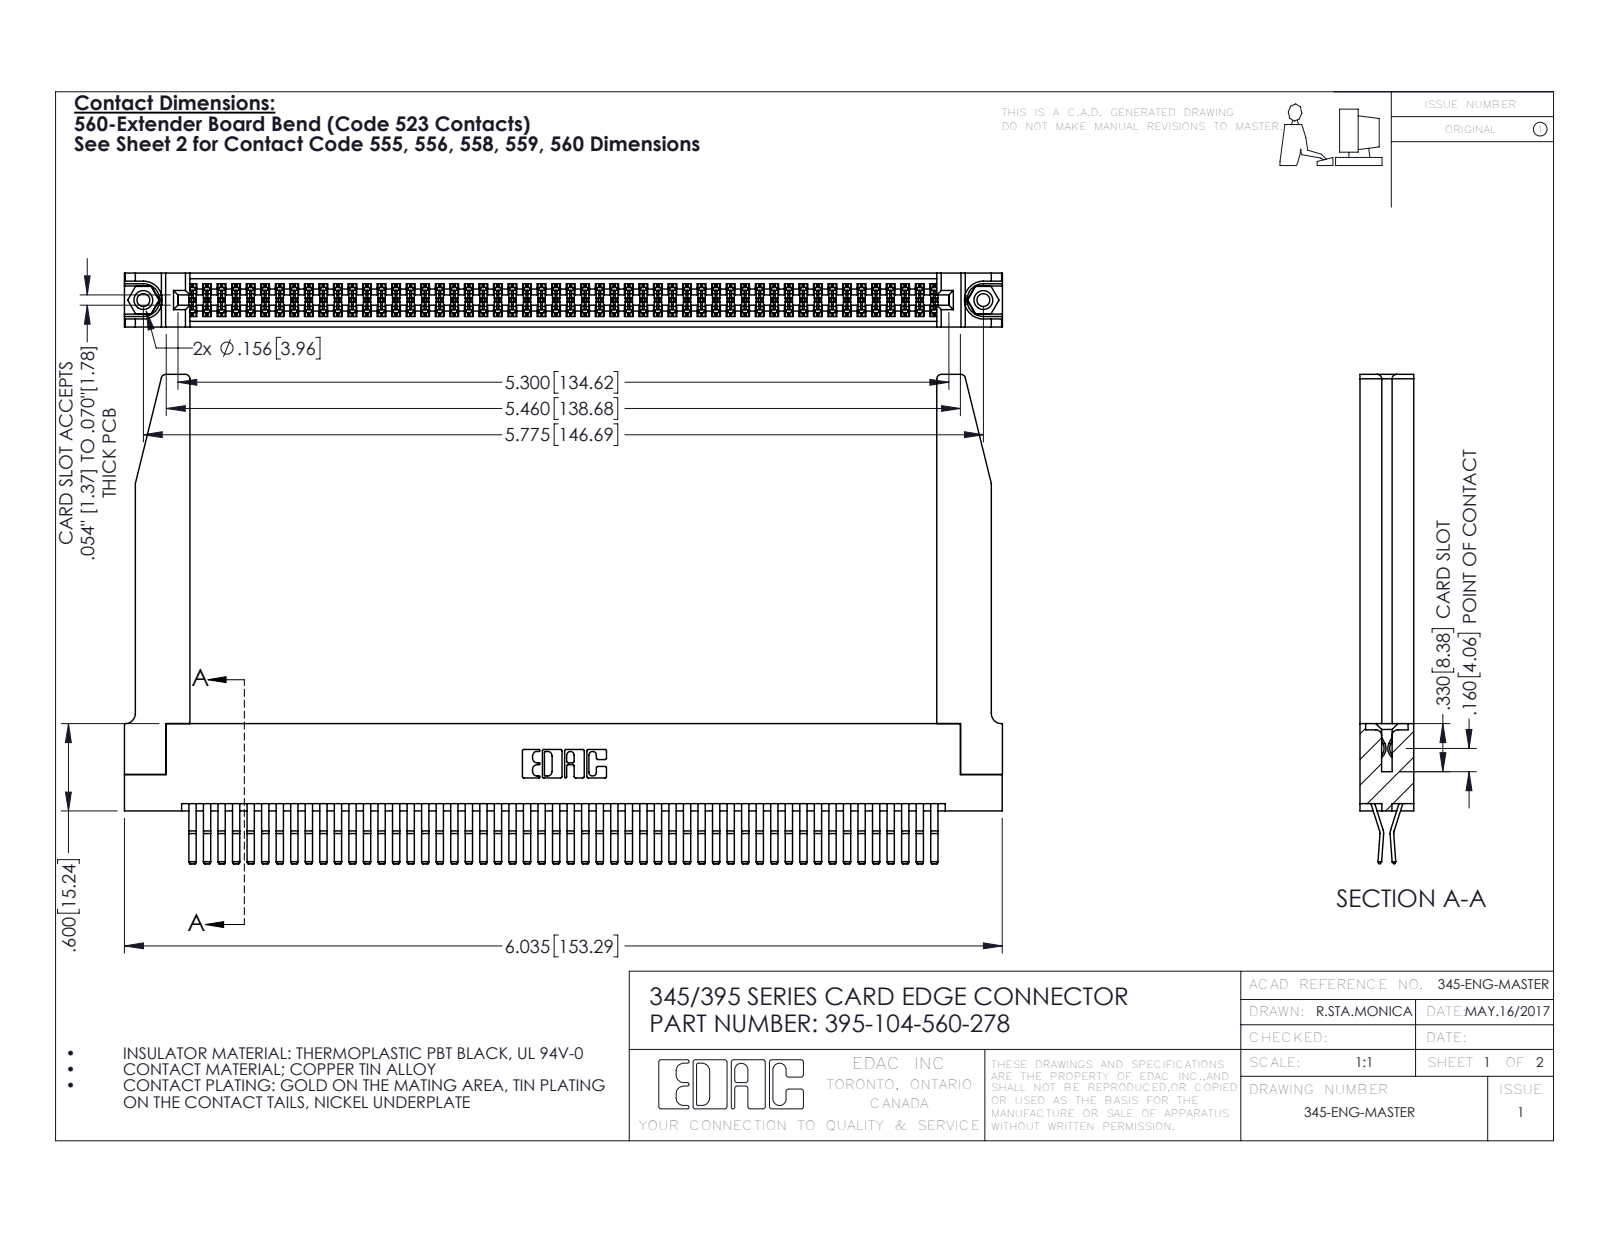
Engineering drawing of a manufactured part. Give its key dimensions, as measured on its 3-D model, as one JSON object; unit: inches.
{"part_name": "345-292-001_560 Tail; 345-220-078_345-220-078; 345-250-001_345-250-001-102; 395-104-560-278 (+1 more)", "step_written_by": "SolidWorks 2016 (CONFIG_CONTROL_DESIGN)", "units": "inches", "bodies": {"solids": 109, "faces": 5768, "planar": 3654, "cylindrical": 2062, "other": 52}, "overall_size": [6.036, 3.362, 0.37], "volume_in3": 1.43, "surface_area_in2": 49.51, "round_holes": [[0.089, 2], [0.125, 2], [0.156, 2], [0.064, 1]], "round_bosses_or_shafts": [[0.155, 2]], "partial_cylinders_radius": [[0.006, 156], [0.01, 22], [0.03, 8], [0.007, 6], [0.031, 6], [0.026, 3], [0.01, 2], [0.014, 2]], "face_to_face_distances": [0.072, 0.37, 0.298, 0.025, 0.2, 0.098, 0.272, 0.225, 0.175, 0.15], "hole_center_spacings": [0.27, 5.539, 5.775]}
